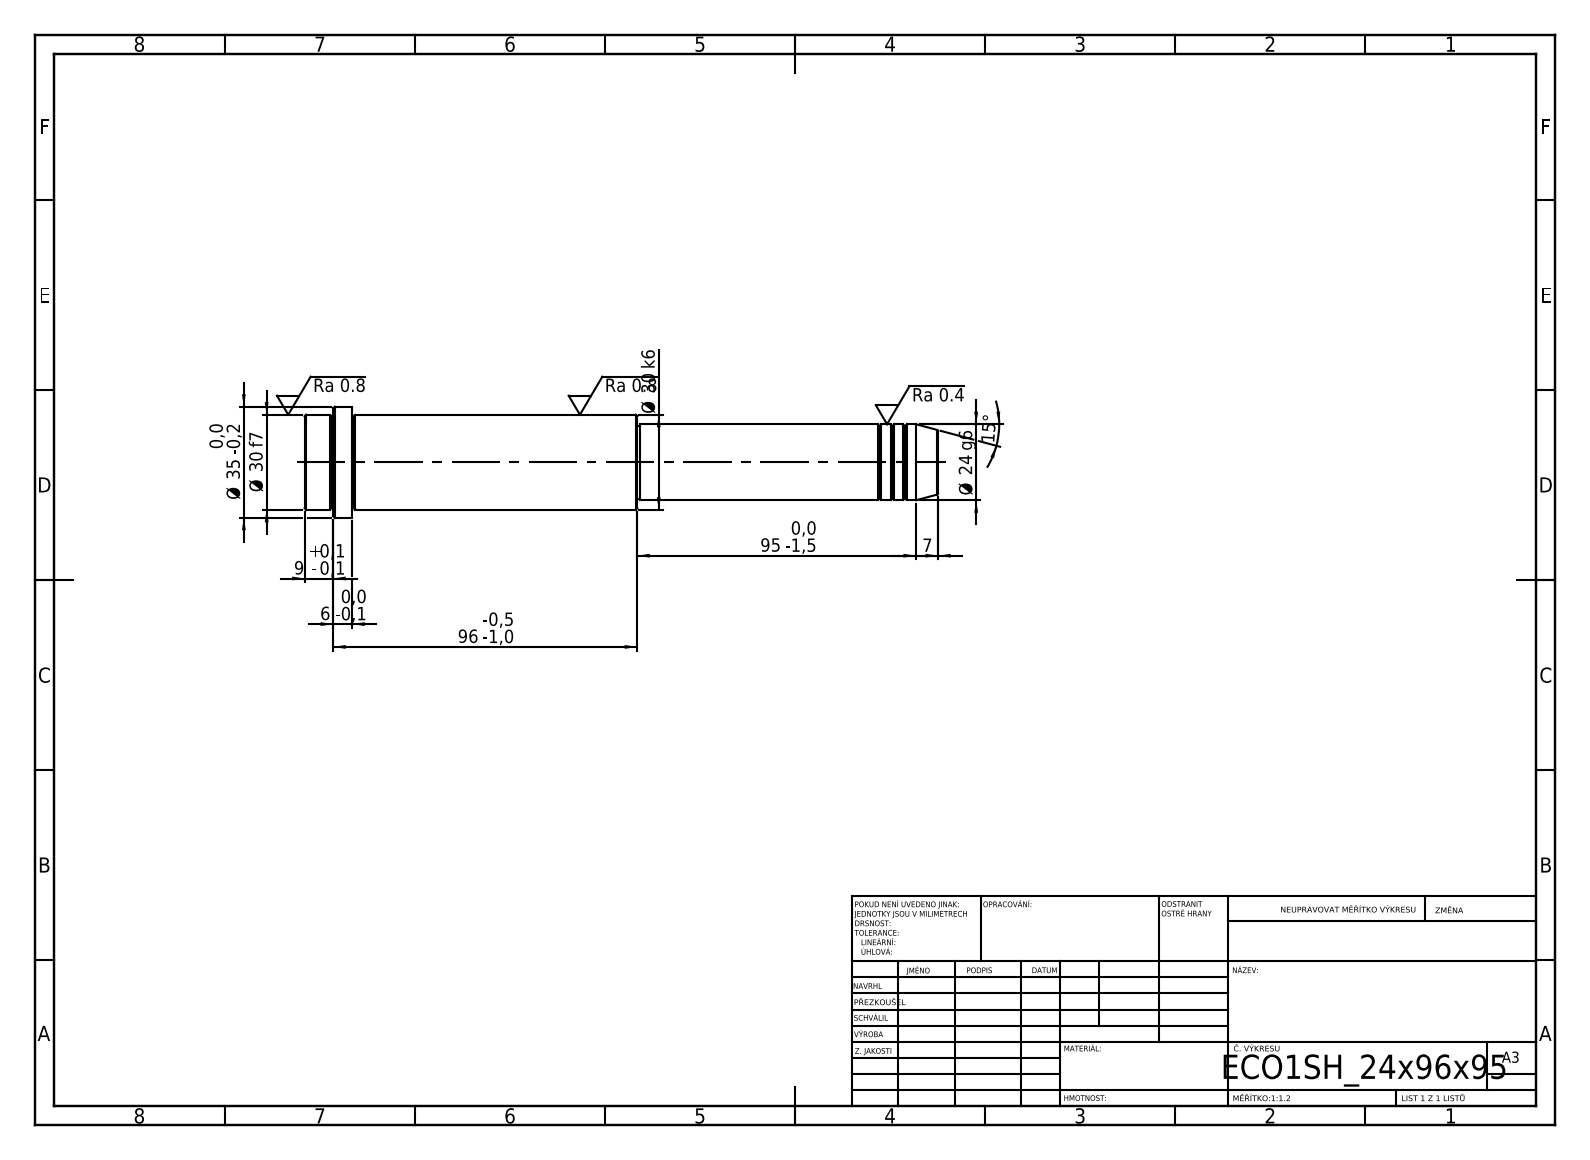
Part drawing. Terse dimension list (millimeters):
written by: SolidWorks 2019 (CONFIG_CONTROL_DESIGN)
unit: mm
bodies: 1 solid, 52 faces (6 planar, 16 cylindrical, 30 other)
size: 200 × 35 × 35
volume: 118 024 mm³; area: 19 119 mm²
bosses: 1× ⌀35, 1× ⌀30, 1× ⌀24, 1× ⌀23
face distances: 200, 185, 15, 95, 90, 105, 191, 96, 6, 9
